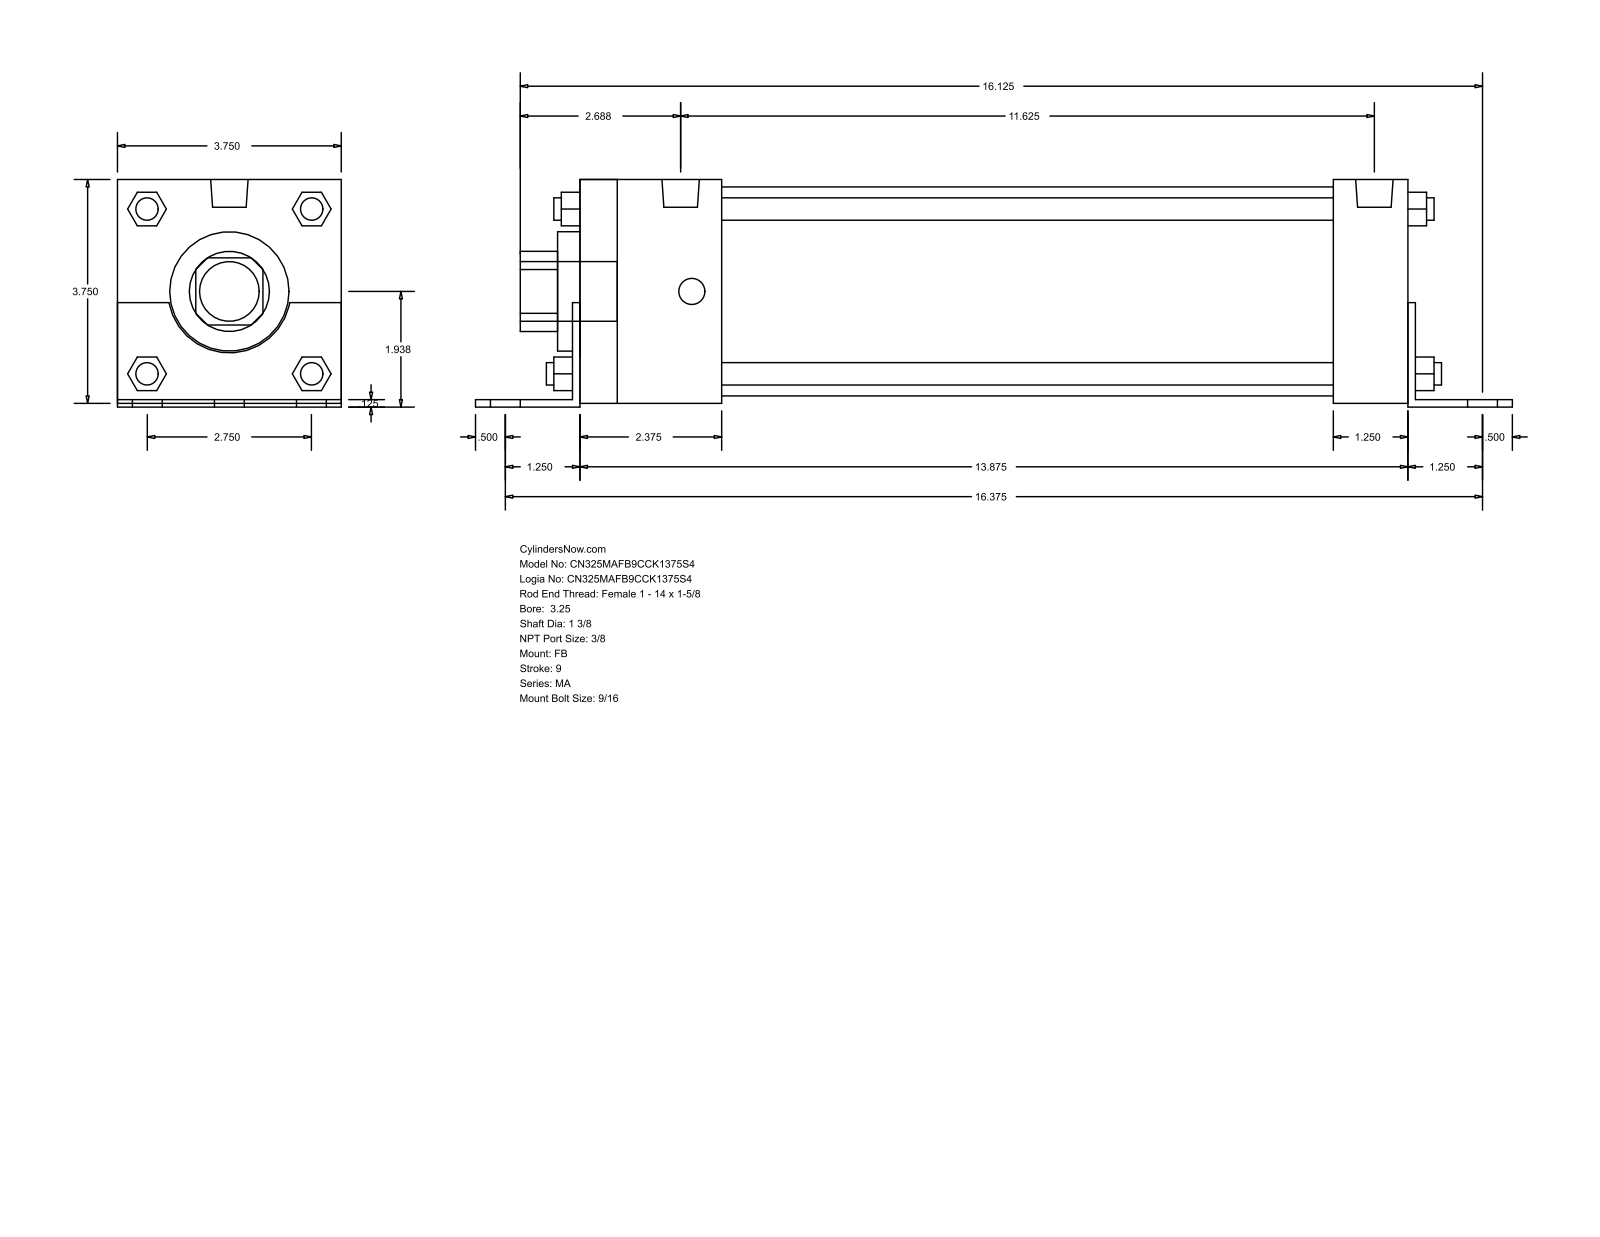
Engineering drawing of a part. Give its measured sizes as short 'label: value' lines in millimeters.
name: MA_FB__0325_1.375
written by: GSSL Pune (CONFIG_CONTROL_DESIGN)
unit: mm
bodies: 0 solids, 140 faces (105 planar, 35 cylindrical, 0 other)
size: 441.32 × 96.84 × 95.25
holes: 1× ⌀34.92, 1× ⌀50.8, 1× ⌀88.9
bosses: 6× ⌀14.29, 4× ⌀11.11, 4× ⌀9.53, 2× ⌀15.93, 1× ⌀25.4
rounds: 1× R17.06, 1× R26.16
face distances: 95.24, 3.17, 1.59, 96.83, 1.58, 93.66, 3.18, 352.42, 355.6, 31.75
